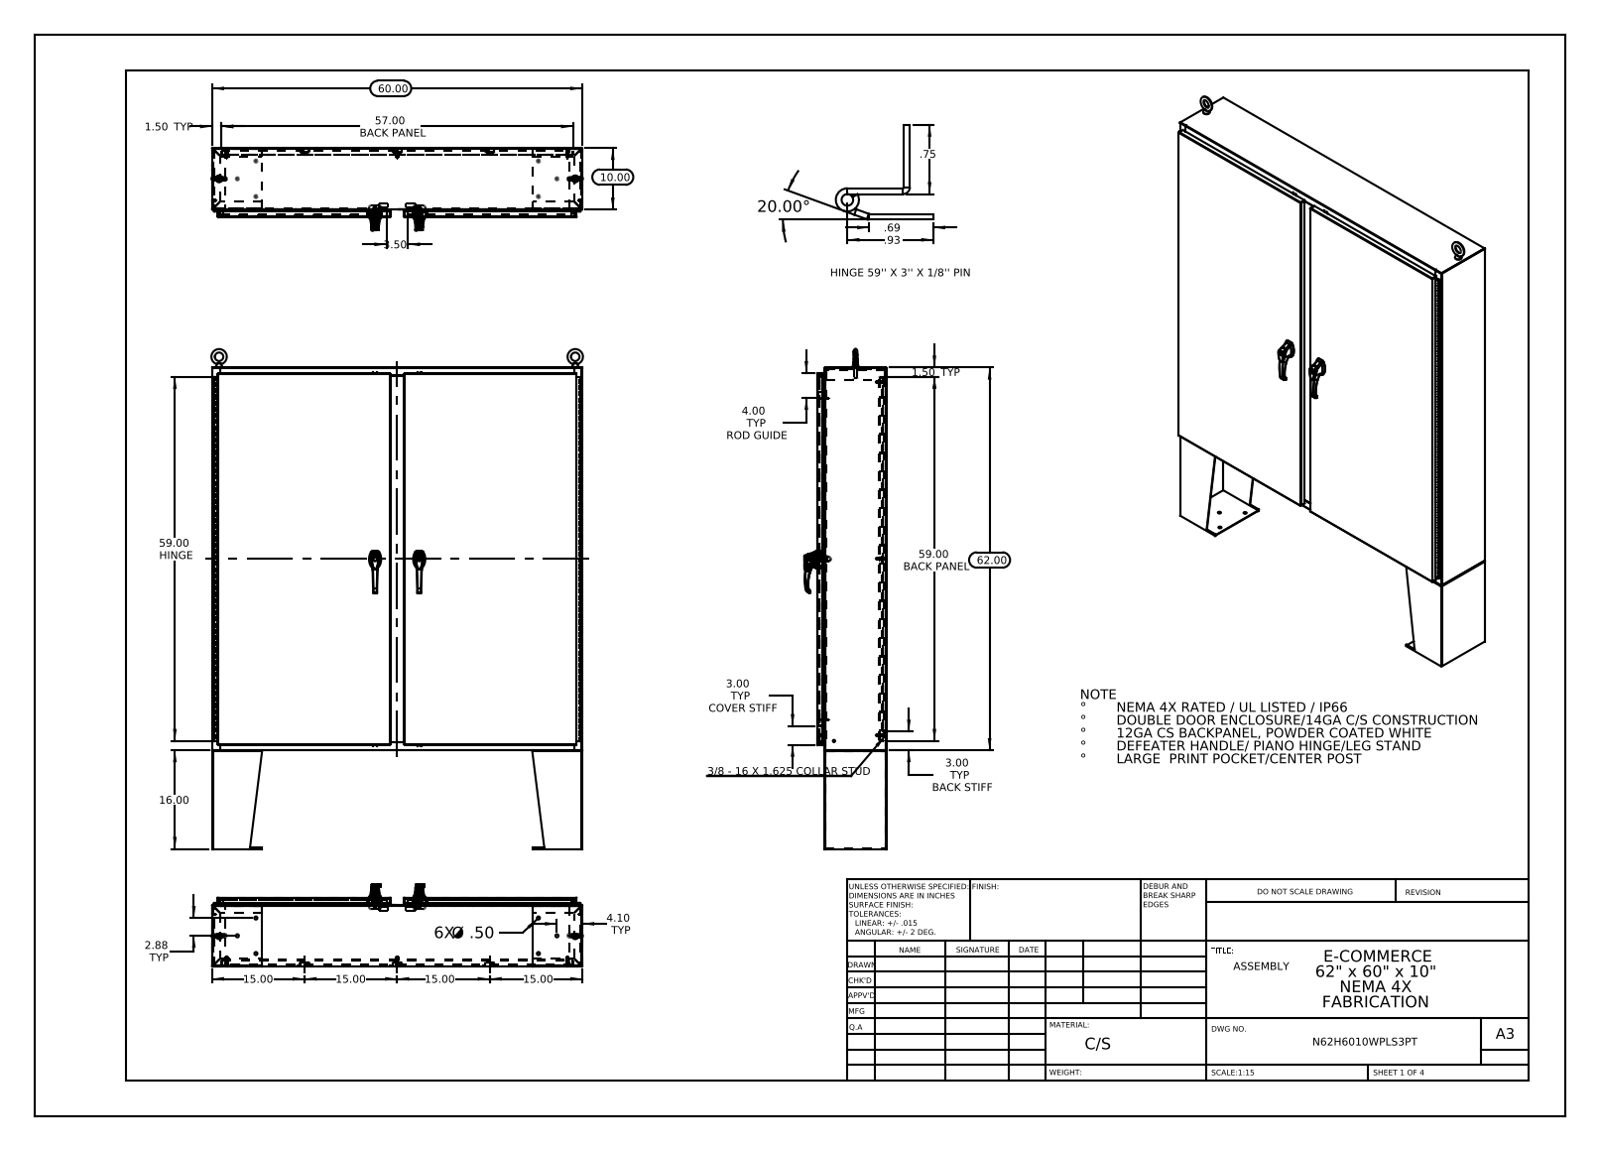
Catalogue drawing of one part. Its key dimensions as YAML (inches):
part_name: "263033_Industrilas; 022151; N62H6010SSWPLS3PT Hinge Cover Side DoubleDoor; N62H6010SSWPLS3PT Bottom (+8 more)"
step_written_by: "SolidWorks 2013 (CONFIG_CONTROL_DESIGN)"
units: inches
bodies: {solids: 82, faces: 7016, planar: 2786, cylindrical: 2770, other: 1460}
overall_size: [81, 60.226, 13.307]
volume: 1390
surface_area: 33604
round_holes:
  - {diameter: 0.25, count: 20}
  - {diameter: 0.5, count: 14}
  - {diameter: 0.138, count: 6}
  - {diameter: 0.161, count: 6}
  - {diameter: 0.079, count: 4}
  - {diameter: 0.313, count: 4}
  - {diameter: 0.437, count: 4}
  - {diameter: 0.75, count: 4}
  - {diameter: 0.125, count: 2}
  - {diameter: 0.125, count: 2}
  - {diameter: 0.197, count: 2}
  - {diameter: 0.203, count: 2}
round_bosses_or_shafts:
  - {diameter: 0.157, count: 12}
  - {diameter: 0.14, count: 12}
  - {diameter: 0.625, count: 10}
  - {diameter: 0.375, count: 8}
  - {diameter: 0.33, count: 8}
  - {diameter: 0.315, count: 5}
  - {diameter: 0.236, count: 5}
  - {diameter: 1.181, count: 2}
partial_cylinders:
  - {radius: 0.118, count: 72}
  - {radius: 0.006, count: 66}
  - {radius: 0.013, count: 46}
  - {radius: 0.088, count: 38}
  - {radius: 0.039, count: 28}
  - {radius: 0.028, count: 24}
  - {radius: 0.008, count: 12}
  - {radius: 0.02, count: 12}
face_to_face_distances: [0.075, 11.126, 0.104, 11.051, 1.075, 11.201, 1, 10.051, 10.126, 1.179]
hole_center_spacings: [7.152, 24.366, 0.295, 0.625, 0.841, 1.313, 1.561, 4.158]
